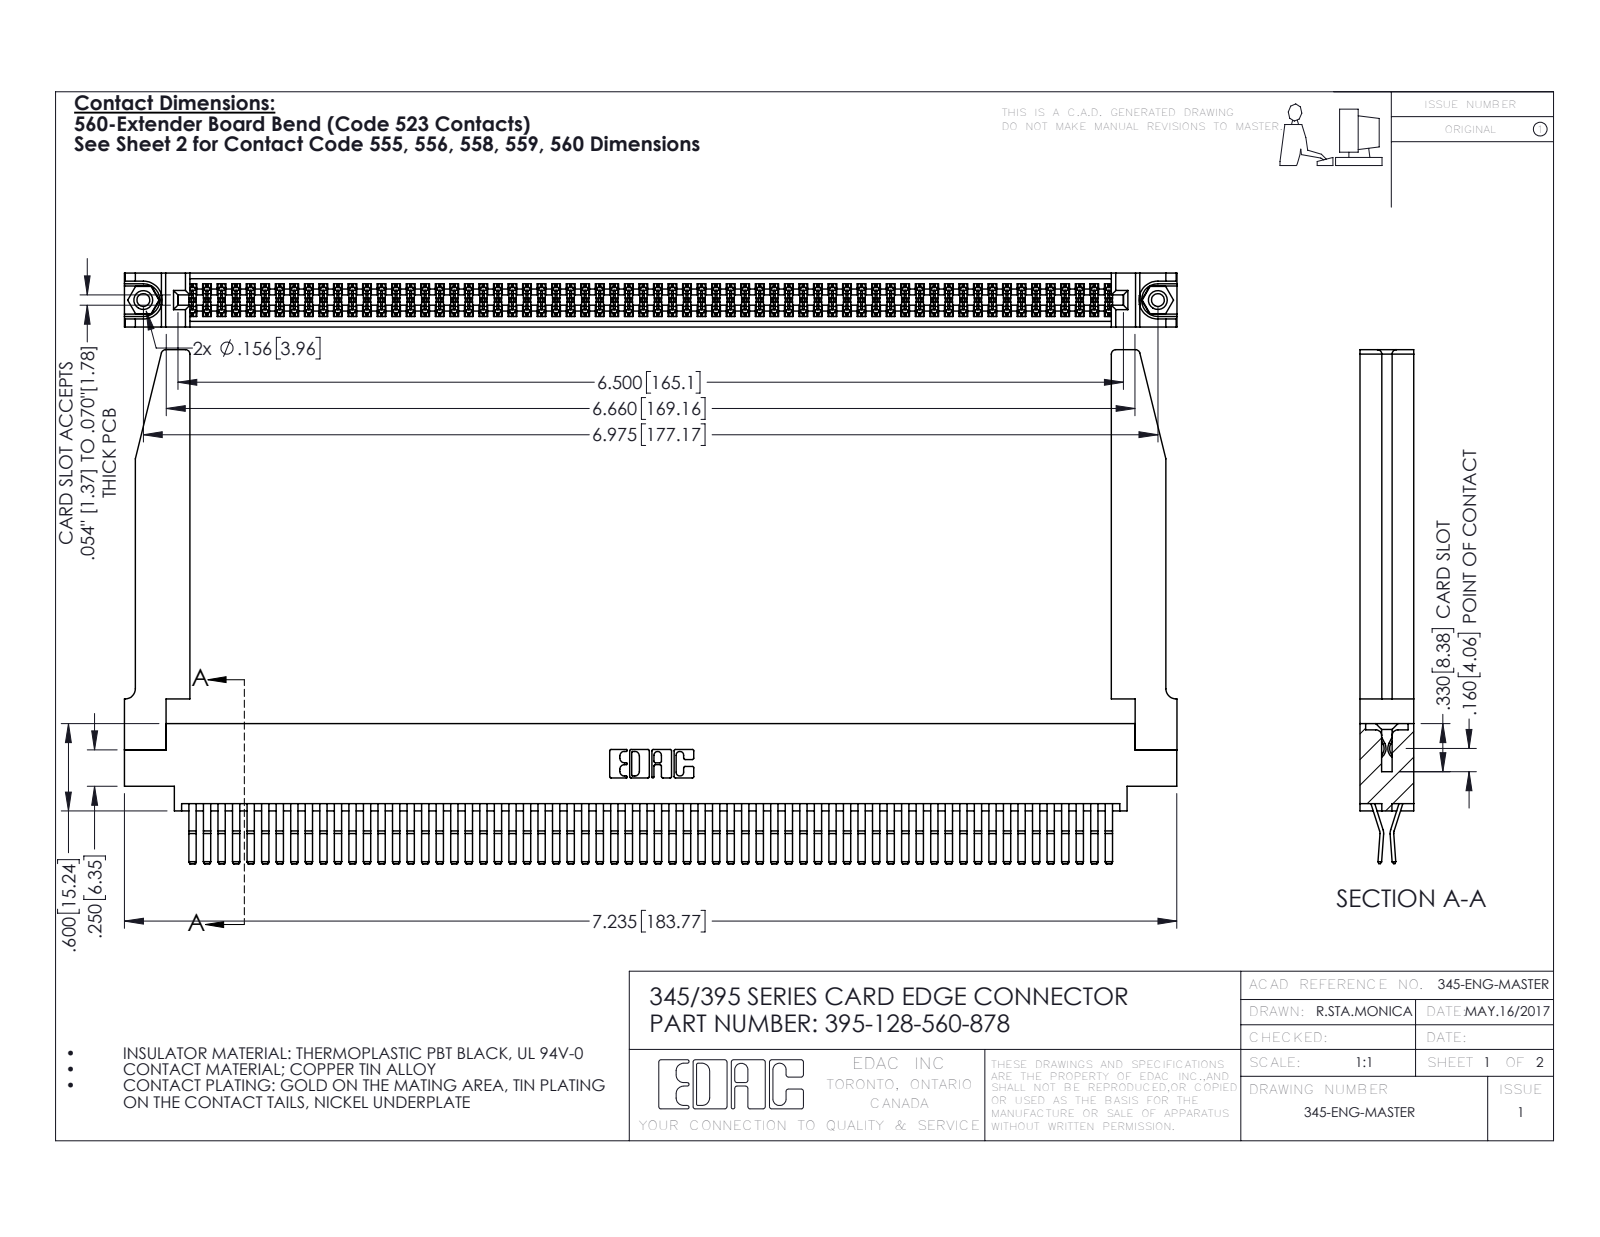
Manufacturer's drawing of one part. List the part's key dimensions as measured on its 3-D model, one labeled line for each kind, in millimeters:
Part name (STEP PRODUCT): 345-250-001_345-250-001-102; 395-128-560-878; 345-292-001_560 Tail; 345-220-078_345-220-078 (+1 more)
STEP written by: SolidWorks 2016 (CONFIG_CONTROL_DESIGN)
Units: millimetres
Bodies: 133 solids, 7020 faces (4450 planar, 2518 cylindrical, 52 other)
Overall size (bounding box): 183.8 × 89.7 × 9.4
Volume: 26 550 mm³ · Surface area: 37 330 mm²
Round holes (diameter × count): ⌀2.3 ×2, ⌀3.2 ×2, ⌀4 ×2, ⌀1.6 ×1
Round bosses / shafts (diameter × count): ⌀3.9 ×2
Partial cylindrical surfaces — rounded edges, fillets, slot ends (radius × count): R0.2 ×192, R0.3 ×22, R0.8 ×8, R0.2 ×6, R0.8 ×6, R0.7 ×3, R0.3 ×2, R0.4 ×2
Main face-to-face distances: 1.8, 9.4, 7.6, 0.6, 2.5, 6.9, 5.1, 5.7, 4.4, 3.8
Hole centre spacings: 6.9, 171.2, 177.2
